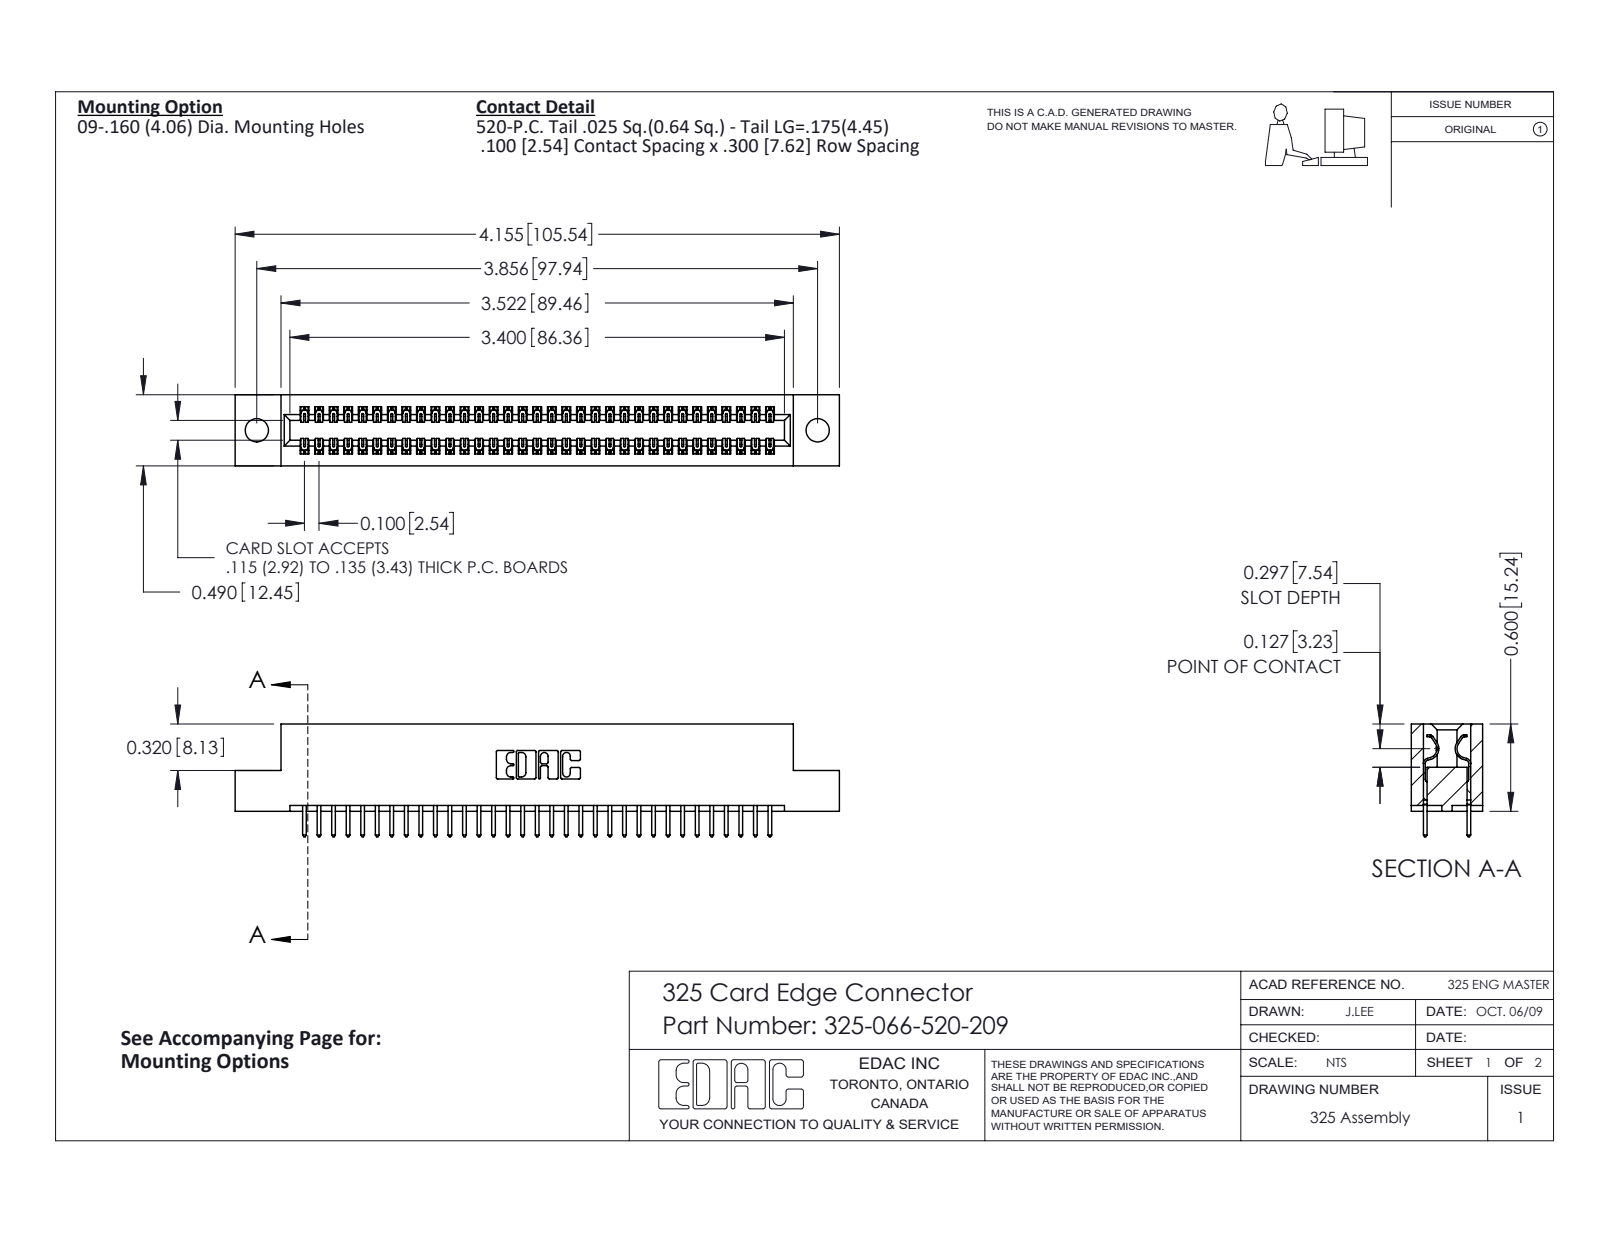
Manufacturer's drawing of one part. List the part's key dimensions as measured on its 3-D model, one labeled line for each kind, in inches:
Part name (STEP PRODUCT): 325 Part_.160 TH; 325-292-001_325-293-120; 325-066-520-209
STEP written by: SolidWorks 2016 (CONFIG_CONTROL_DESIGN)
Units: inches
Bodies: 67 solids, 3546 faces (2446 planar, 1100 cylindrical, 0 other)
Overall size (bounding box): 4.155 × 0.775 × 0.49
Volume: 0.812 in³ · Surface area: 24.3 in²
Round holes (diameter × count): ⌀0.16 ×2
Partial cylindrical surfaces — rounded edges, fillets, slot ends (radius × count): R0.006 ×99, R0.01 ×66, R0.01 ×22, R0.007 ×6, R0.031 ×6, R0.026 ×3, R0.014 ×2, R0.022 ×2
Main face-to-face distances: 0.083, 0.407, 0.49, 0.3, 0.107, 0.383, 0.025, 0.325, 0.275, 0.56
Hole centre spacings: 3.856
